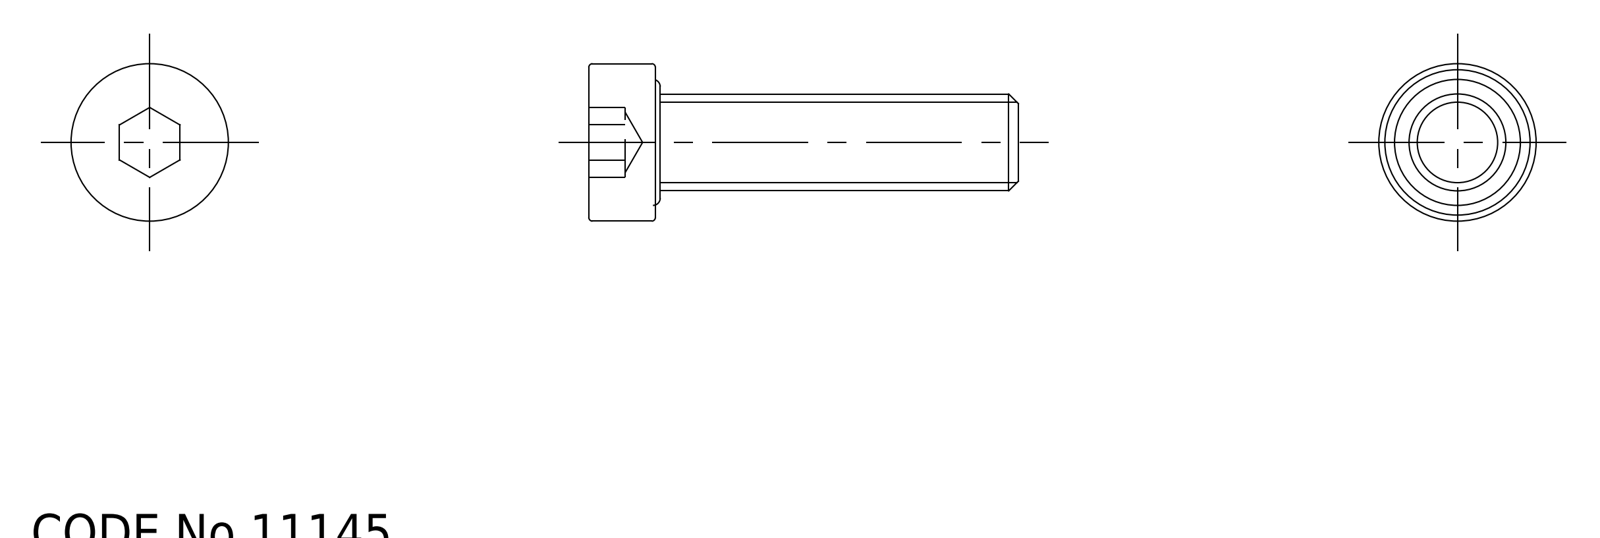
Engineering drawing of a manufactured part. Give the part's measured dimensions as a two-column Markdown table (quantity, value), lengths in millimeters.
| quantity | value |
| --- | --- |
| part name | screw; TL_418_M8_30 |
| STEP written by | SolidWorks 2015 (AUTOMOTIVE_DESIGN) |
| units | millimeters |
| bodies | 2 solids, 27 faces (11 planar, 6 cylindrical, 10 other) |
| overall size | 35.5 × 13 × 13 |
| volume | 2 146 mm³ |
| surface area | 1 432 mm² |
| round holes (diameter × count) | 12 × 1 |
| round bosses / shafts (diameter × count) | 13 × 1, 8 × 1 |
| main face-to-face distances | 4.7, 35.5, 30.8, 5, 3, 1.7, 32.5, 5.5, 2.5, 0.8 |
